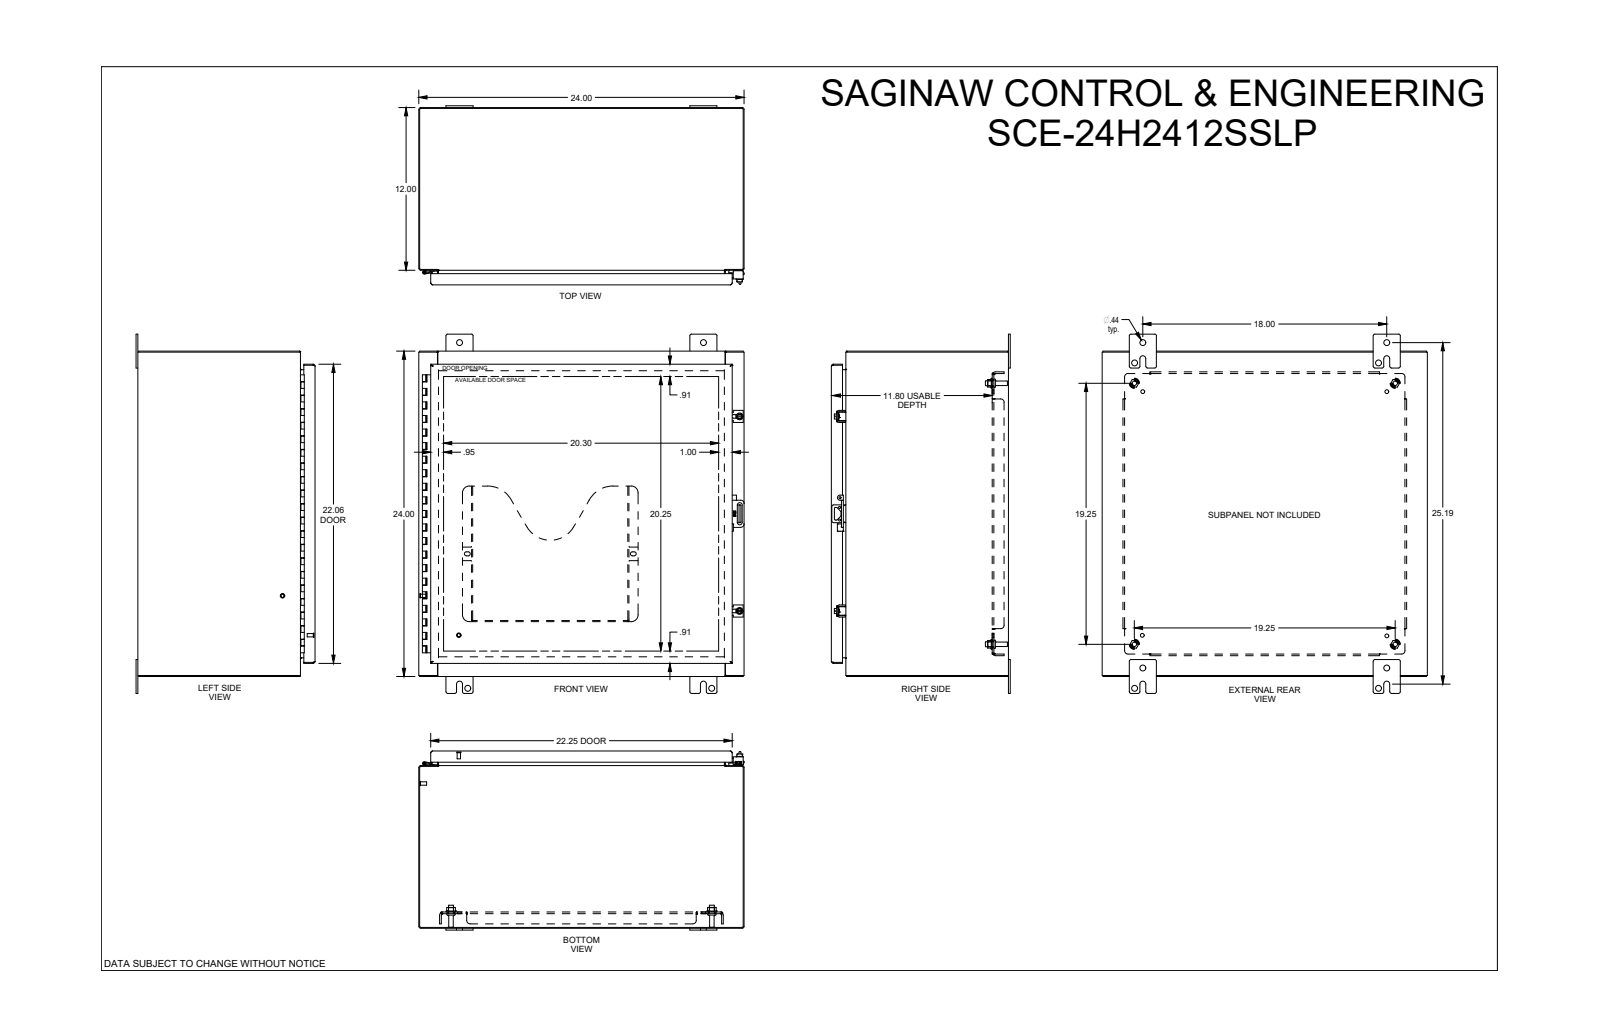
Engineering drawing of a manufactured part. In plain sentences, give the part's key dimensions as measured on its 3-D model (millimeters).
The part is named "SCE-24H2412SSLP". Its 3-D file was written by "SolidWorks 2019 (CONFIG_CONTROL_DESIGN)". It is 0 solids with 3192 faces: 1285 planar, 670 cylindrical and 1237 other. Overall it measures 673.1 by 609.6 by 335.5 millimeters. Round holes: 8 of diameter 11.1, 5 of diameter 6.4, 4 of diameter 4.8, 4 of diameter 4.9, 4 of diameter 7.1, 4 of diameter 9.3, 4 of diameter 12.7, 2 of diameter 4.1, 2 of diameter 5.2, 1 of diameter 3.3, 1 of diameter 3.4. Round bosses or shafts: 7 of diameter 6.3, 5 of diameter 14.3, 4 of diameter 9.3, 4 of diameter 8.4, 4 of diameter 6.5, 4 of diameter 4.8, 3 of diameter 6.4, 2 of diameter 12.9. Partial cylindrical surfaces (rounded edges, fillets, slot ends): 114 of radius 0.3, 36 of radius 0.4, 30 of radius 0.7, 27 of radius 0.8, 27 of radius 3.2, 25 of radius 1.5, 22 of radius 1, 14 of radius 1.8. The main face-to-face distances are 1.9, 607.7, 605.8, 609.6, 330.1, 328.2, 1.9, 30.5, 301.6, 332.1. The hole center spacings are 473.5, 22.2, 457.2, 489, 165.1, 669.2, 13.1, 36.6.
